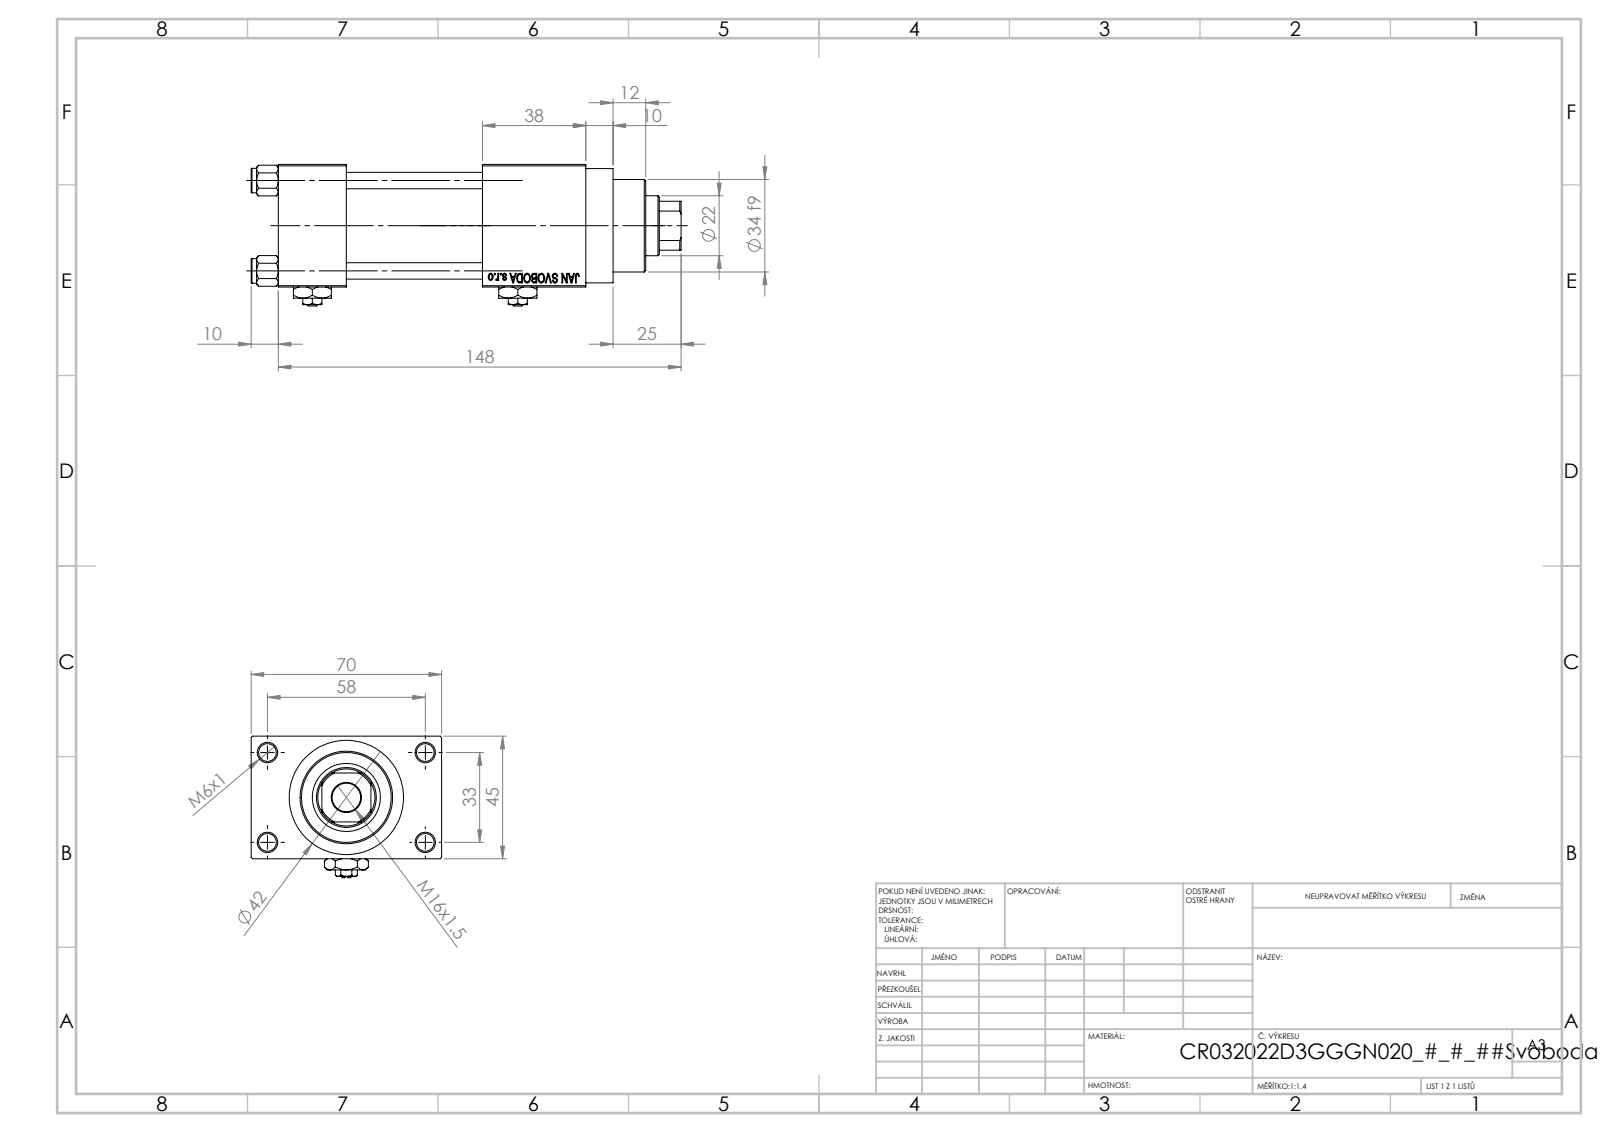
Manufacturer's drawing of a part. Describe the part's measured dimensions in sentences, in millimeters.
The part is named "V215_VC_A; Zatka_pro_OIL_PORT; V215CR_D_Body; V215CR_VCP_D (+2 more)". Its 3-D file was written by "SolidWorks 2019 (CONFIG_CONTROL_DESIGN)". It is 13 solids with 1202 faces: 542 planar, 100 cylindrical and 560 other. Overall it measures 158 by 70 by 52 millimeters. Its volume is 243 368 cubic millimeters and its surface area 81 200 square millimeters. Round holes: 4 of diameter 6, 4 of diameter 6.5, 2 of diameter 7, 2 of diameter 13.16, 2 of diameter 20, 1 of diameter 10.5, 1 of diameter 22, 1 of diameter 24, 1 of diameter 25, 1 of diameter 32, 1 of diameter 33. Round bosses or shafts: 4 of diameter 9, 1 of diameter 42, 1 of diameter 38, 1 of diameter 34. Partial cylindrical surfaces (rounded edges, fillets, slot ends): 1 of radius 10.5. The main face-to-face distances are 45, 25, 12.5, 57.5, 50, 75, 88, 70, 38, 113. The hole center spacings are 12.4, 23.48, 33.2, 33.37, 35.35, 45.6, 56.35, 33.
